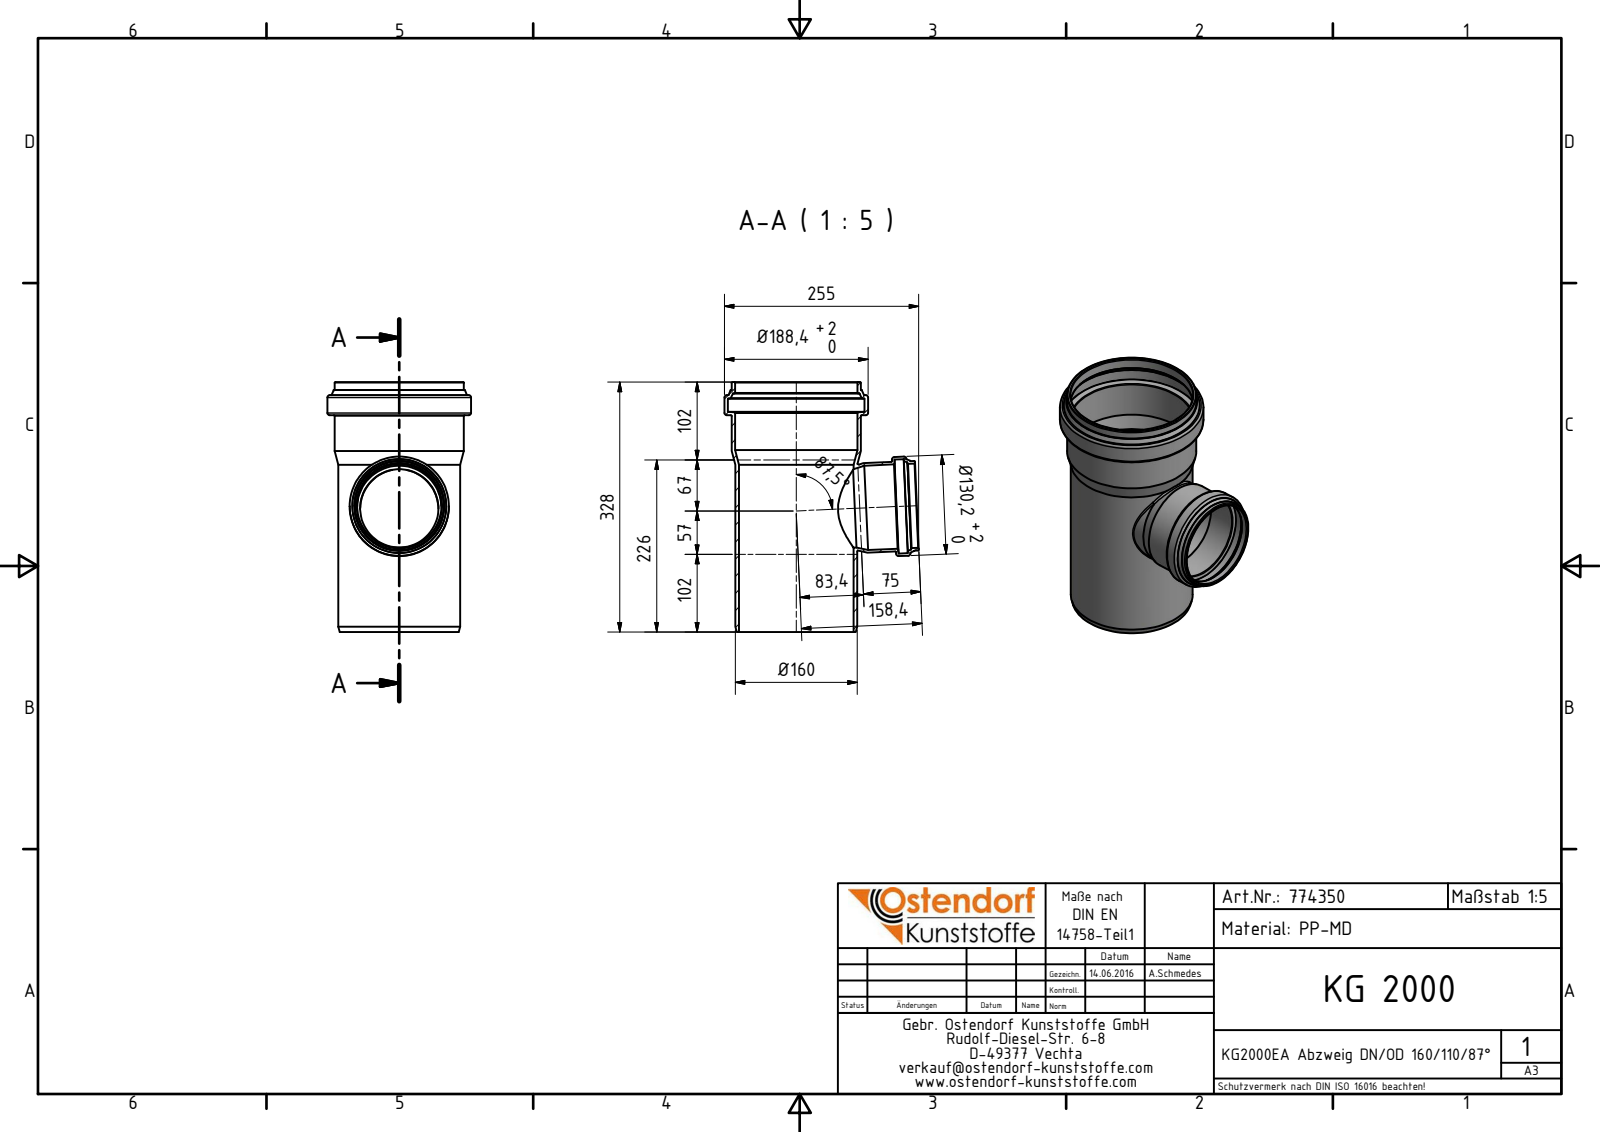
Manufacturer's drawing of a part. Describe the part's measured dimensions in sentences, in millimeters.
The part is named "774350 KG2000EA Abzweig DN_OD 160_110_87°". Its 3-D file was written by "Autodesk Inventor 2016 (AUTOMOTIVE_DESIGN)". It is 1 solid with 70 faces: 8 planar, 17 cylindrical and 45 other. Overall it measures 328 by 255 by 188.4 millimeters. Its volume is 897 661 cubic millimeters and its surface area 401 645 square millimeters. Round holes: 2 of diameter 110.8, 1 of diameter 102.7, 1 of diameter 123.4, 1 of diameter 150.3, 1 of diameter 160.7, 1 of diameter 179.4. Round bosses or shafts: 2 of diameter 117.6, 1 of diameter 188.4, 1 of diameter 169.7, 1 of diameter 160.1, 1 of diameter 130.2. Partial cylindrical surfaces (rounded edges, fillets, slot ends): 1 of radius 55.05. The main face-to-face distances are 284.5, 328, 43.5, 310.8, 26.3, 17.2, 29.9, 317.5, 33, 6.7.
